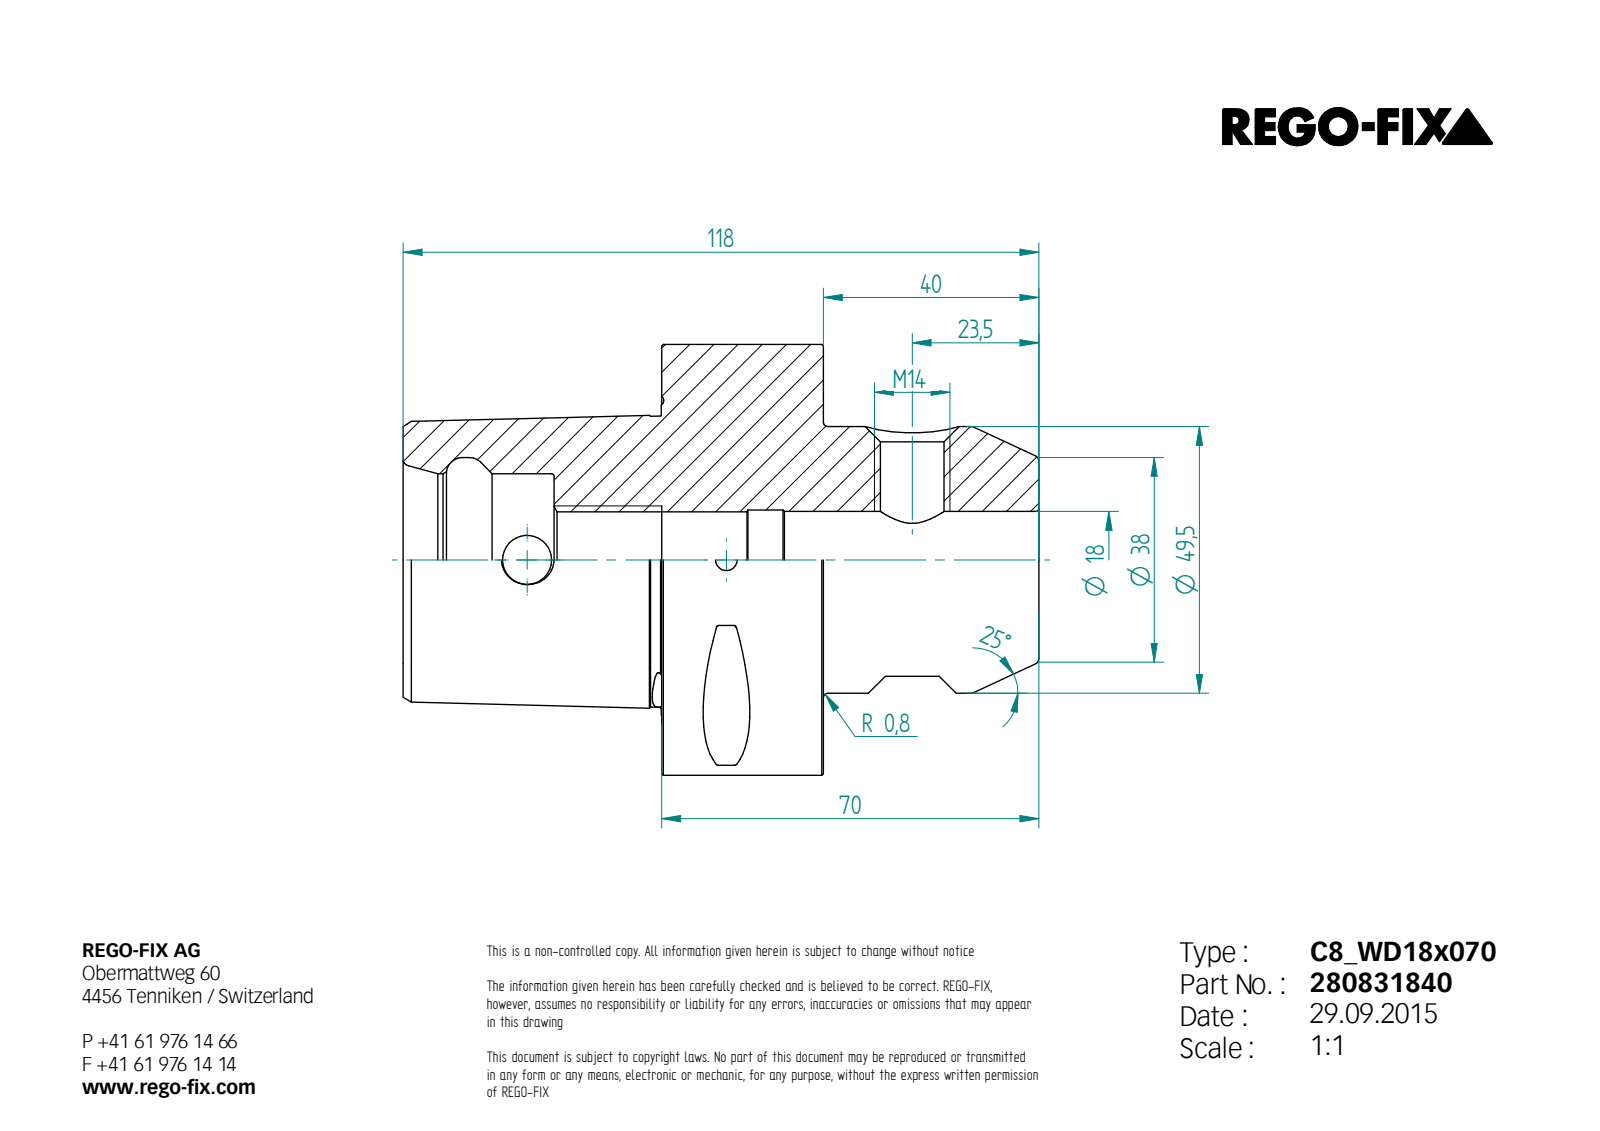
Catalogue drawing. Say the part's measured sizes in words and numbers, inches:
Its 3-D file was written by "Unknown (AUTOMOTIVE_DESIGN)". It is 1 solid with 104 faces: 23 planar, 21 cylindrical and 60 other. Overall it measures 4.646 by 3.15 by 3.15 inches. Its volume is 16.8 cubic inches and its surface area 61.26 square inches. Round holes: 1 of diameter 0.157, 1 of diameter 0.358, 1 of diameter 0.466, 1 of diameter 0.702, 1 of diameter 0.709, 1 of diameter 0.728, 1 of diameter 1.26, 1 of diameter 1.496. Round bosses or shafts: 1 of diameter 3.15, 1 of diameter 1.949. Partial cylindrical surfaces (rounded edges, fillets, slot ends): 8 of radius 0.02. The main face-to-face distances are 1.181, 1.89, 3.071, 4.646, 2.756, 1.575, 1.281, 1.102, 0.787, 1.969. The hole center spacings are 1.457.
